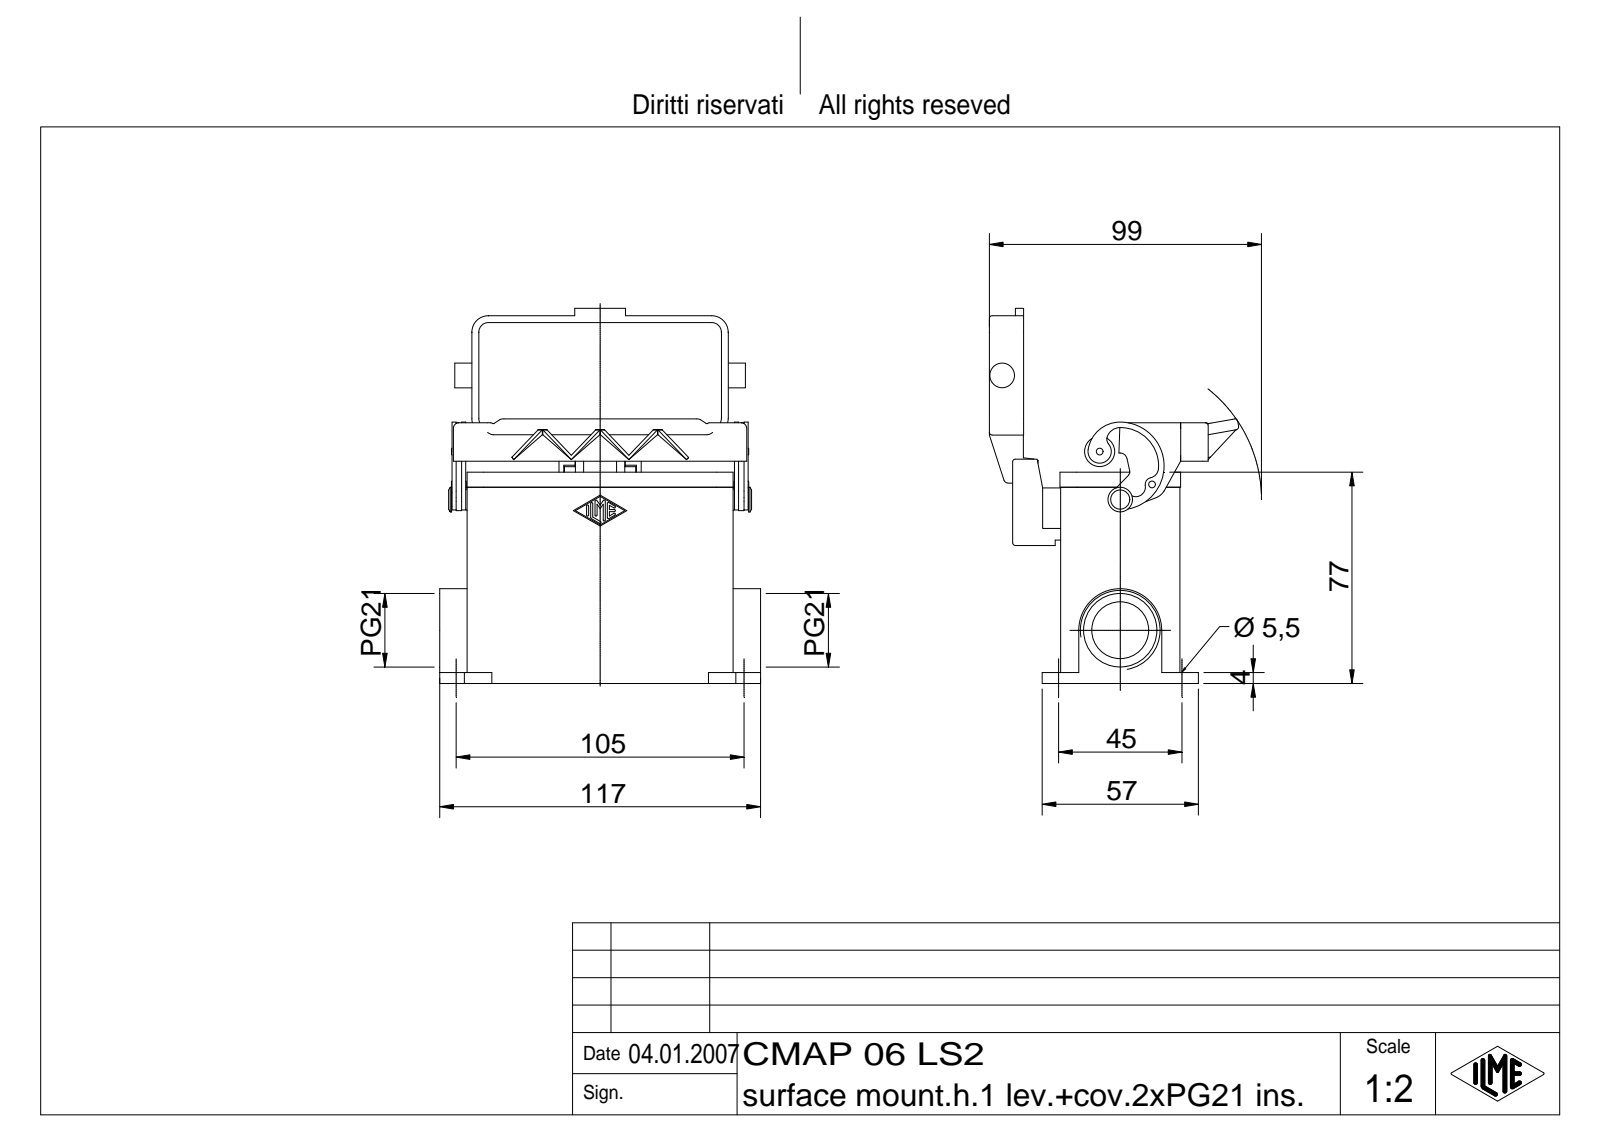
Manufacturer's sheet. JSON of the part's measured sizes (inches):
{"part_name": "CMAP 06 LS2", "step_written_by": "Autodesk Inventor 7 (AUTOMOTIVE_DESIGN)", "units": "inches", "bodies": {"solids": 6, "faces": 609, "planar": 265, "cylindrical": 180, "other": 164}, "overall_size": [5.382, 4.606, 3.581], "volume_in3": 9.875, "surface_area_in2": 132.5, "round_holes": [[0.217, 4], [0.079, 1], [0.157, 1], [0.818, 1], [1.054, 1]], "round_bosses_or_shafts": [[0.354, 2], [0.197, 2], [0.433, 1], [0.276, 1], [0.157, 1], [0.118, 1], [0.098, 1]], "partial_cylinders_radius": [[0.039, 18], [0.015, 14], [0.079, 12], [0.236, 12], [0.059, 6], [0.138, 6], [0.118, 4], [0.02, 3]], "face_to_face_distances": [0.118, 1.594, 1.713, 0.157, 1.476, 1.024, 2.618, 2.736, 1.142, 0.886], "hole_center_spacings": [1.772, 4.134, 4.498, 2.14]}
